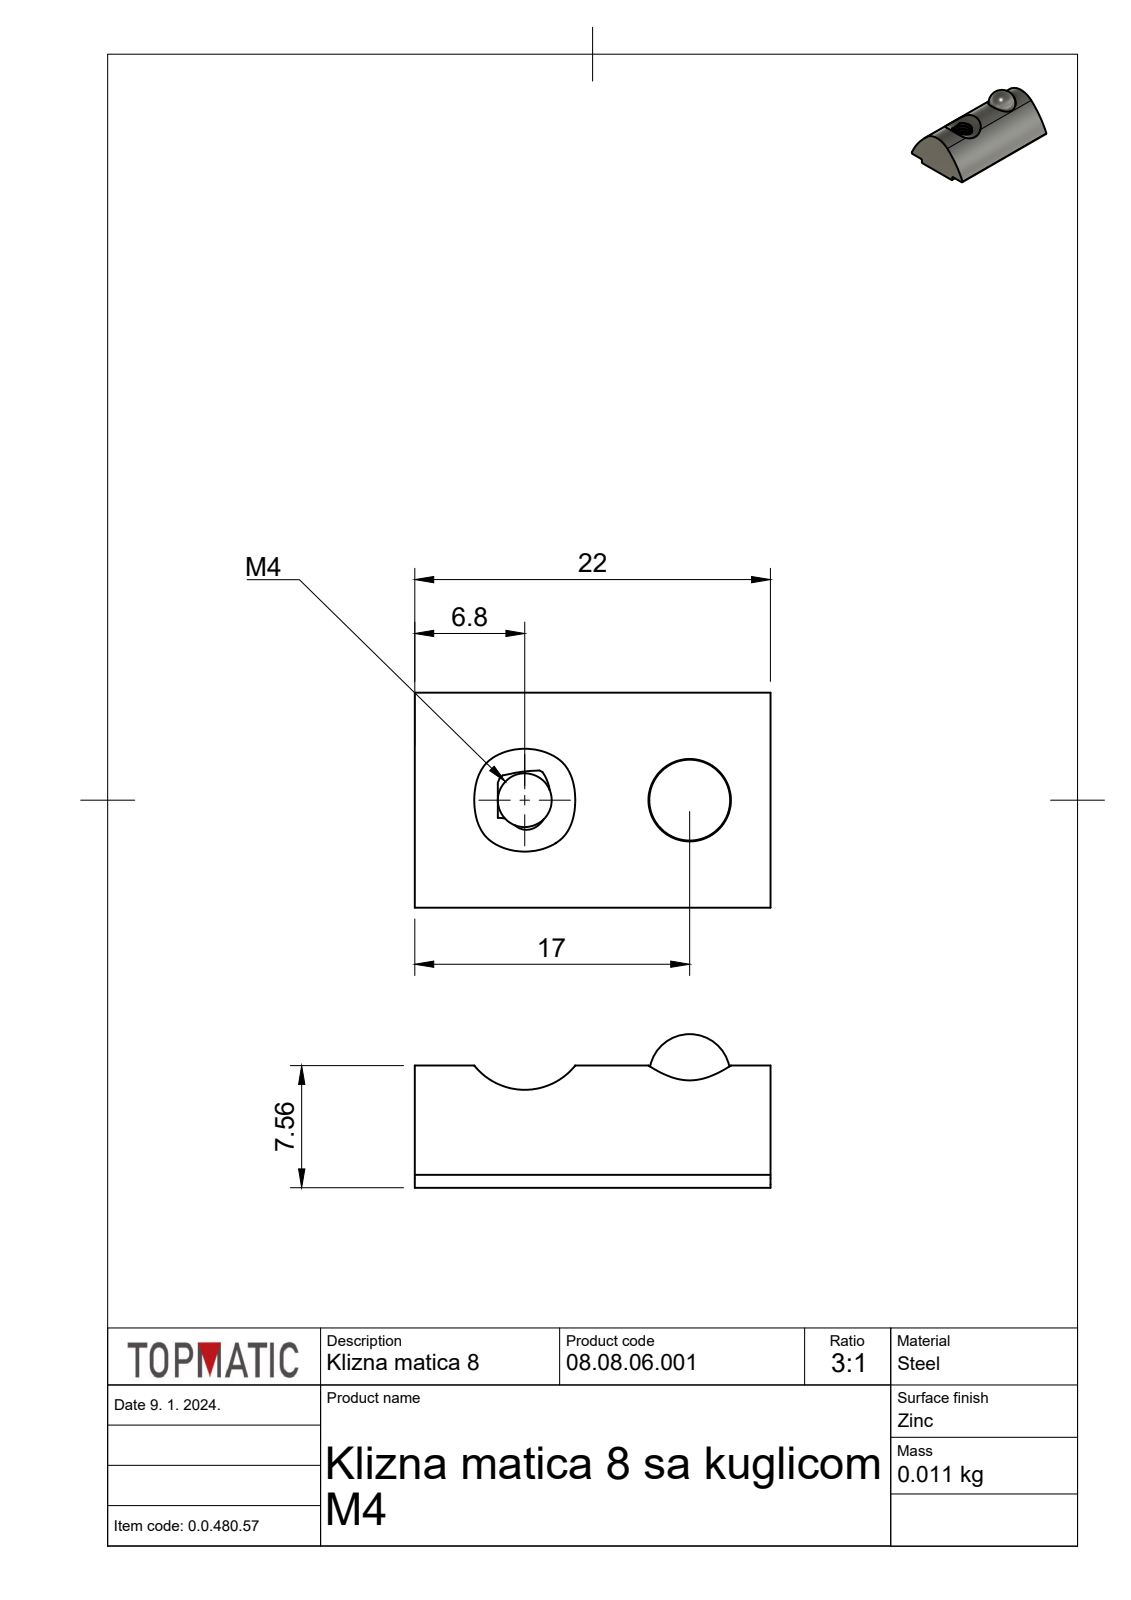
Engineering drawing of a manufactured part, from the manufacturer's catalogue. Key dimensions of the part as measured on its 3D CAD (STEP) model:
Part name (STEP PRODUCT): Klizna matica 8 M4 v1
STEP written by: Autodesk Translation Framework v12.14.0.127 (AUTOMOTIVE_DESIGN)
Units: millimetres
Bodies: 2 solids, 46 faces (8 planar, 32 cylindrical, 6 other)
Overall size (bounding box): 22 × 13.3 × 9.5
Volume: 1 346 mm³ · Surface area: 1 145 mm²
Round holes (diameter × count): ⌀3.33 ×1, ⌀4.11 ×1, ⌀5.1 ×1
Partial cylindrical surfaces — rounded edges, fillets, slot ends (radius × count): R0.2 ×6, R4 ×2, R16 ×2
Main face-to-face distances: 0.8, 22, 8, 5.62, 6.42
Hole centre spacings: 10.2
